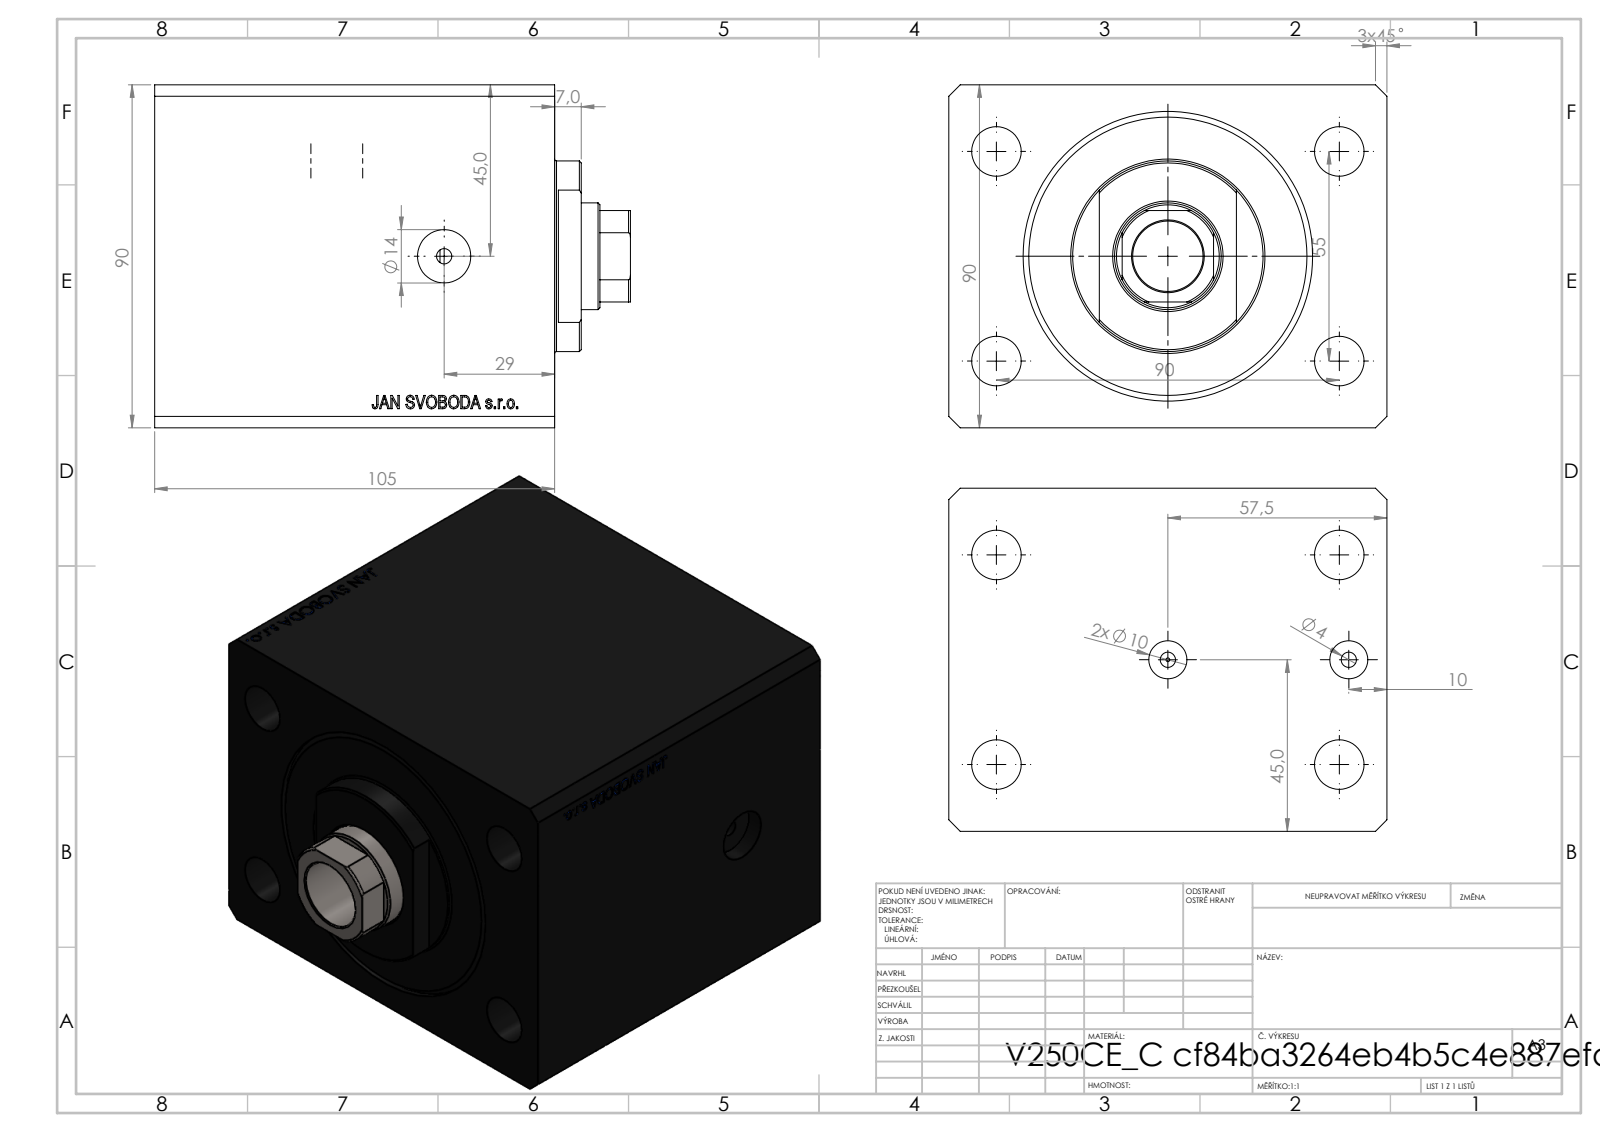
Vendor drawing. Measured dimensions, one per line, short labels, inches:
name: V250CE_C_Body; V250CE_VC_C; V250CE_C_VCP
written by: SolidWorks 2019 (CONFIG_CONTROL_DESIGN)
unit: in
bodies: 3 solids, 868 faces (428 planar, 46 cylindrical, 394 other)
size: 4.917 × 4.528 × 3.543
volume: 60.09 in³; area: 218.5 in²
holes: 4× ⌀0.157, 4× ⌀0.512, 2× ⌀0.394, 2× ⌀0.551, 1× ⌀0.049, 1× ⌀0.728, 1× ⌀1.102, 1× ⌀2.48, 1× ⌀2.992
bosses: 1× ⌀1.969
rounds: 1× R0.531
face distances: 3.543, 4.528, 4.134, 0.705, 3.429, 2.244, 2.949, 1.185, 2.161, 1.457
hole spacings: 2.076, 1.087, 2.165, 3.543, 3.799, 4.153, 1.85, 1.87
